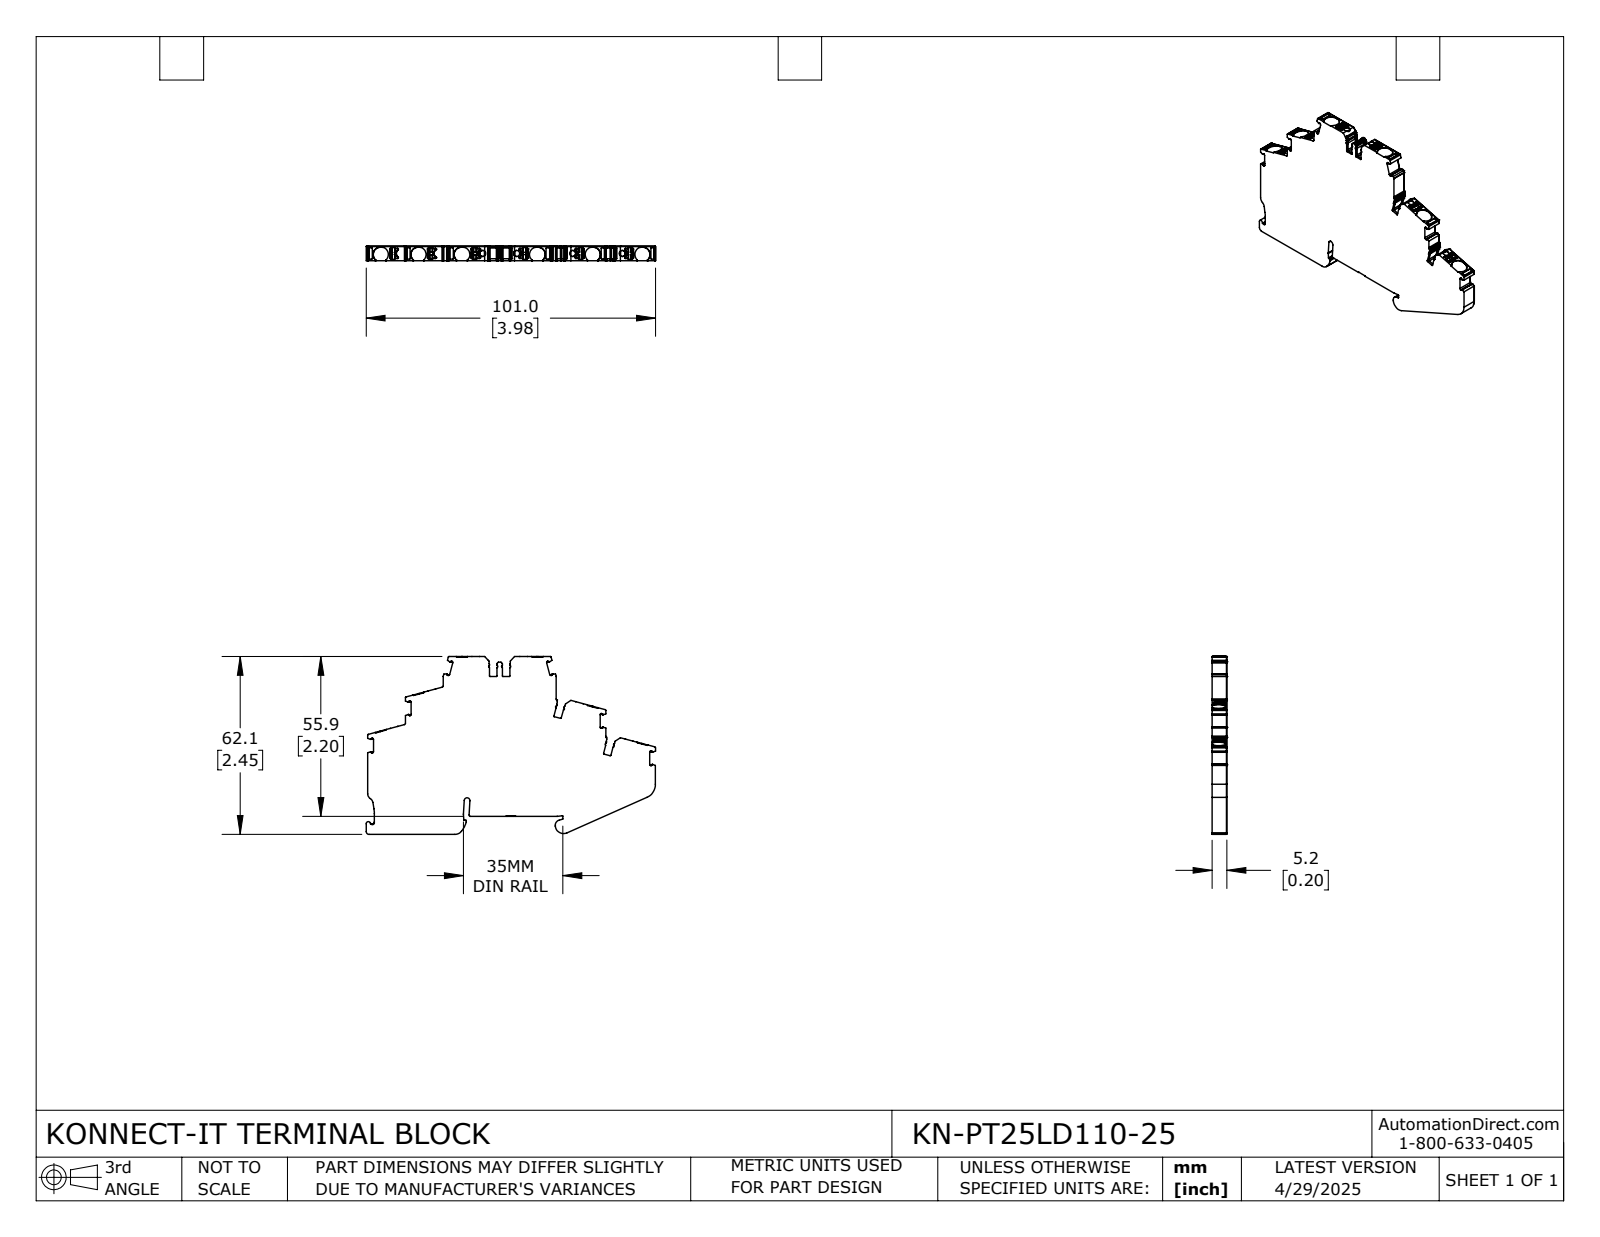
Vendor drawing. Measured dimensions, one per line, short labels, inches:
name: KN-PT25LD110-25
written by: SolidWorks 2024 (CONFIG_CONTROL_DESIGN)
unit: in
bodies: 1 solid, 1212 faces (579 planar, 528 cylindrical, 105 other)
size: 3.977 × 2.445 × 0.203
volume: 1.354 in³; area: 16.76 in²
holes: 4× ⌀0.083
rounds: 128× R0.008, 49× R0.004, 47× R0.012, 26× R0.02, 24× R0.006, 17× R0.016, 14× R0.024, 12× R0.006
face distances: 0.203, 0.246, 0.079, 2.191, 2.437, 0.319, 0.682, 0.519, 2.445, 2.199
hole spacings: 0.466, 0.792
